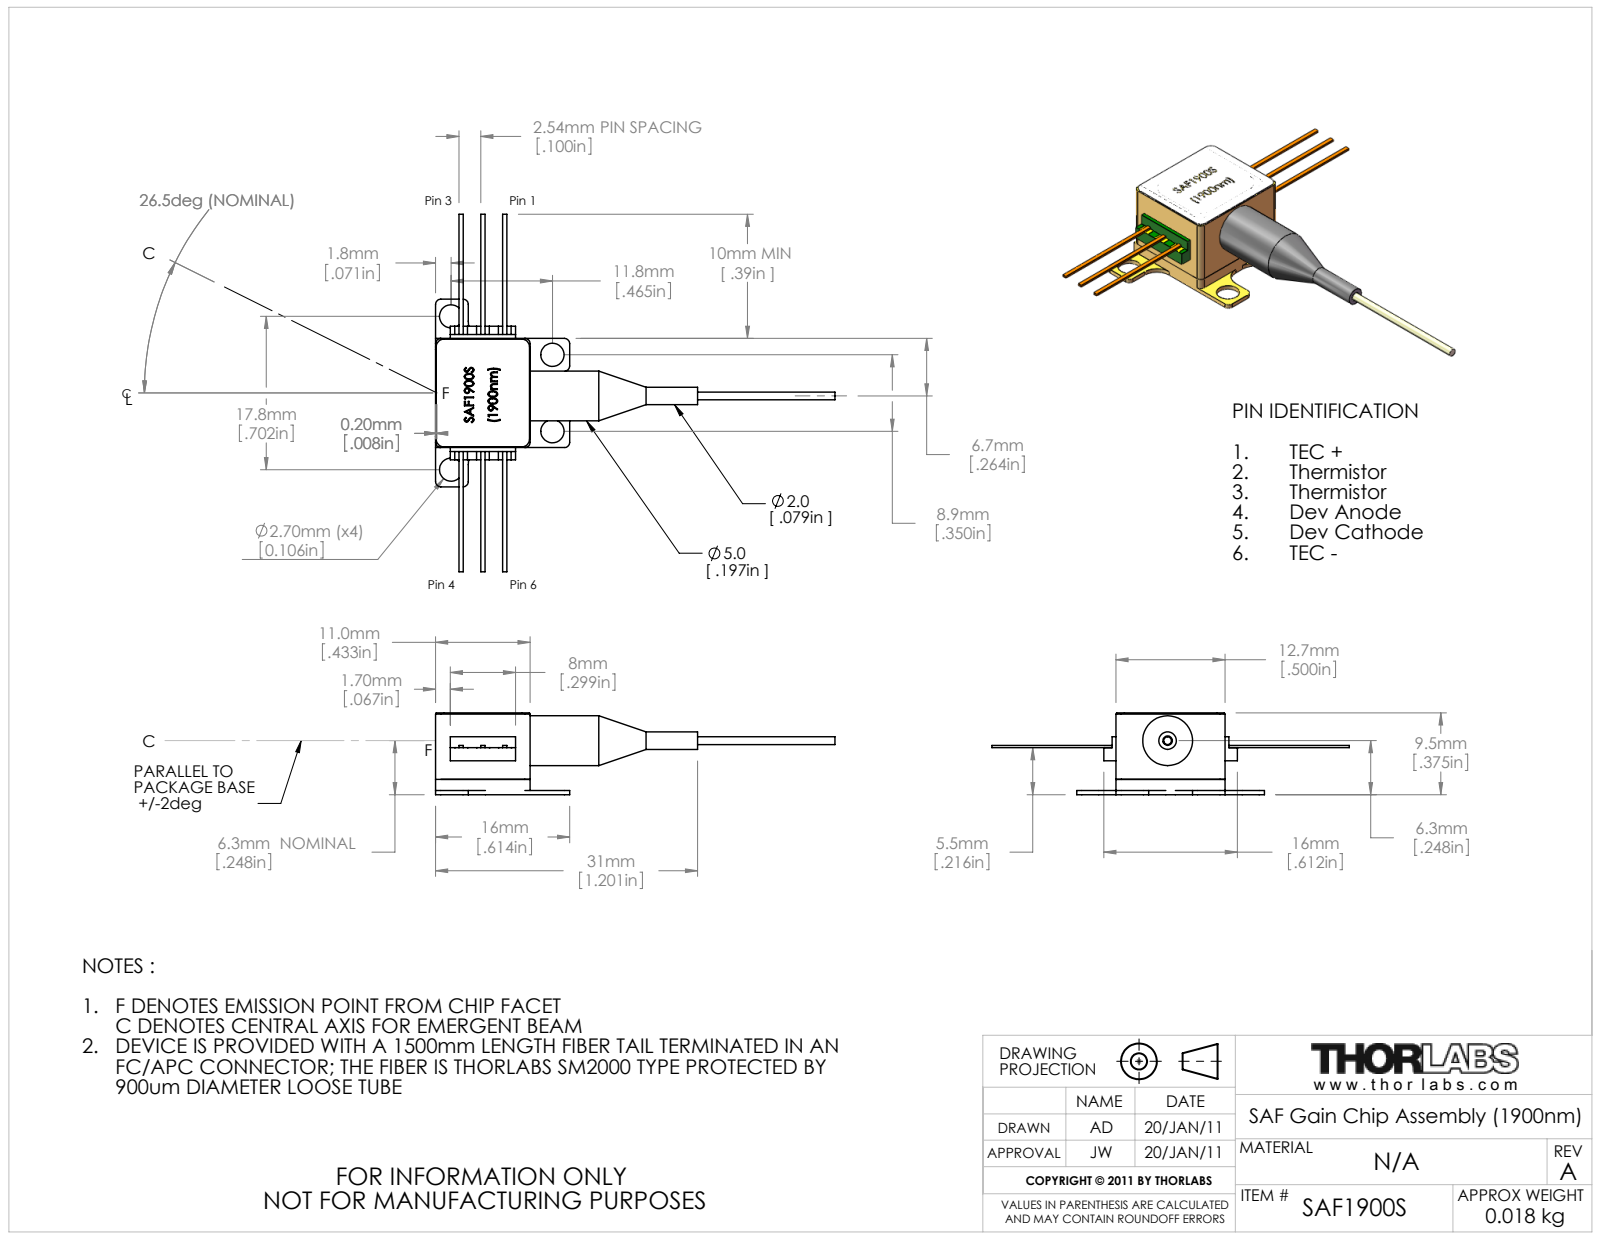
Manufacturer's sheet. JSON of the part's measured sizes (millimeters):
{"part_name": "21586-E0W", "step_written_by": "SolidWorks 2009 (AUTOMOTIVE_DESIGN)", "units": "millimeters", "bodies": {"solids": 15, "faces": 474, "planar": 279, "cylindrical": 70, "other": 125}, "overall_size": [46.5, 41.6, 9.53], "volume_mm3": 946, "surface_area_mm2": 2431, "round_holes": [[2.7, 4], [1.1, 1], [2.08, 1], [3.18, 1], [4.1, 1]], "round_bosses_or_shafts": [[5.8, 1], [3.45, 1], [2.04, 1], [0.9, 1]], "partial_cylinders_radius": [[0.6, 12], [1, 10], [0.13, 4], [0.3, 4], [0.9, 4], [1.85, 4], [2, 4]], "face_to_face_distances": [1, 1.6, 9.52, 7.92, 7.8, 9.4, 7.6, 11.7, 1.8, 7.72], "hole_center_spacings": [12.62, 17.83, 8.9, 17.84]}
